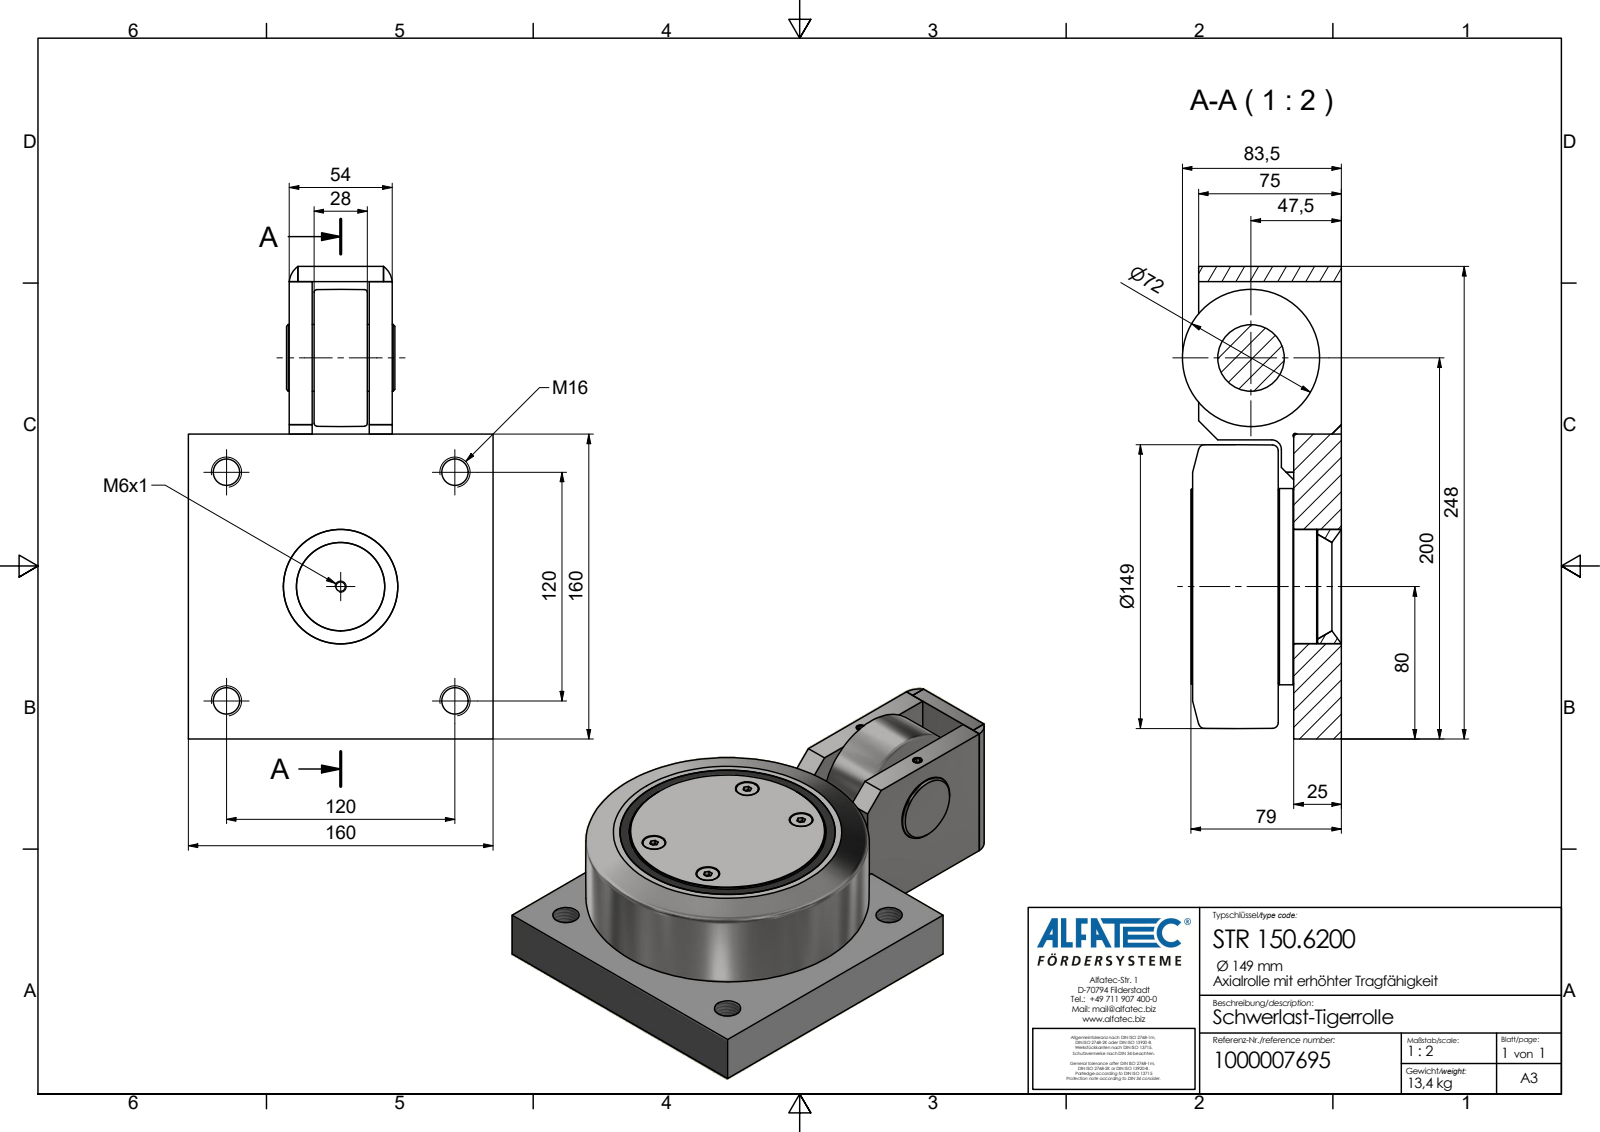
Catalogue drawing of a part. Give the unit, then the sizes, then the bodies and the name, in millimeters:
Units: millimetres
Overall size (bounding box): 248 × 160 × 83.5
Round holes (diameter × count): ⌀12.4 ×4, ⌀13.84 ×4, ⌀4.92 ×2, ⌀35.1 ×1
Round bosses / shafts (diameter × count): ⌀11.7 ×4, ⌀6 ×2, ⌀103 ×1, ⌀102.5 ×1, ⌀101.4 ×1, ⌀35 ×1
Partial cylindrical surfaces — rounded edges, fillets, slot ends (radius × count): R11.03 ×2, R1.2 ×1, R5 ×1
Main face-to-face distances: 25, 54, 42, 12, 53, 65, 95, 107, 33.2, 8.2
Hole centre spacings: 47.36, 83.92, 102.75, 120, 123.92, 40, 69.28, 71.56
Volume: 1 767 000 mm³ · Surface area: 163 951 mm²
Bodies: 1 solid, 136 faces (79 planar, 31 cylindrical, 26 other)
Part name (STEP PRODUCT): STR 150.6200_Kontur
STEP written by: Autodesk Inventor 2020 (AP242_MANAGED_MODEL_BASED_3D_ENGINEERING_MIM_LF)
